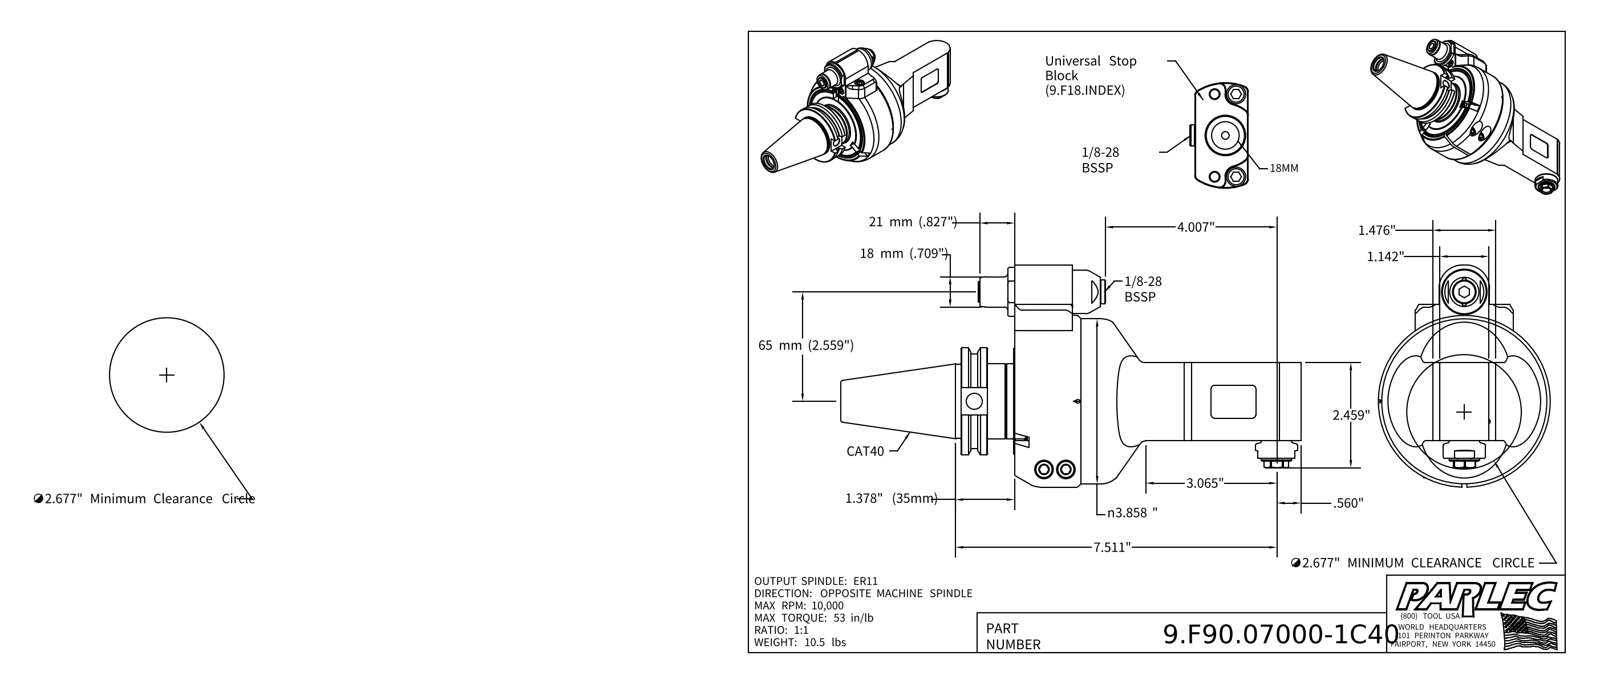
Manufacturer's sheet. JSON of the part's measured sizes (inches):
{"part_name": "9.F90.07000-1C40; 9_F90_07000; 9_GA1_446_2 (EVO, Type 1, C40, 65mm, 35mm)", "step_written_by": "Autodesk Inventor 2022 (AUTOMOTIVE_DESIGN)", "units": "inches", "bodies": {"solids": 4, "faces": 602, "planar": 264, "cylindrical": 175, "other": 163}, "overall_size": [10.758, 5.196, 4.016], "volume_in3": 48.81, "surface_area_in2": 215.4, "round_holes": [[0.335, 21], [0.126, 4], [0.197, 3], [0.256, 3], [0.102, 2], [0.13, 2], [0.165, 2], [0.315, 2], [0.409, 2], [0.433, 2], [0.492, 2], [0.098, 1]], "round_bosses_or_shafts": [[0.394, 4], [0.709, 3], [0.472, 2], [0.315, 2], [0.236, 2], [0.098, 2], [4.016, 1], [3.858, 1]], "partial_cylinders_radius": [[0.039, 14], [0.079, 12], [0.118, 6], [0.157, 4], [0.02, 2], [0.315, 2], [0.551, 2], [0.571, 2]], "face_to_face_distances": [0.02, 0.276, 0.039, 0.295, 1.26, 0.335, 1.831, 1.142, 1.555, 1.28], "hole_center_spacings": [1.516, 1.47, 1.824, 2.144, 3.002, 0.422, 2.651, 2.914]}
